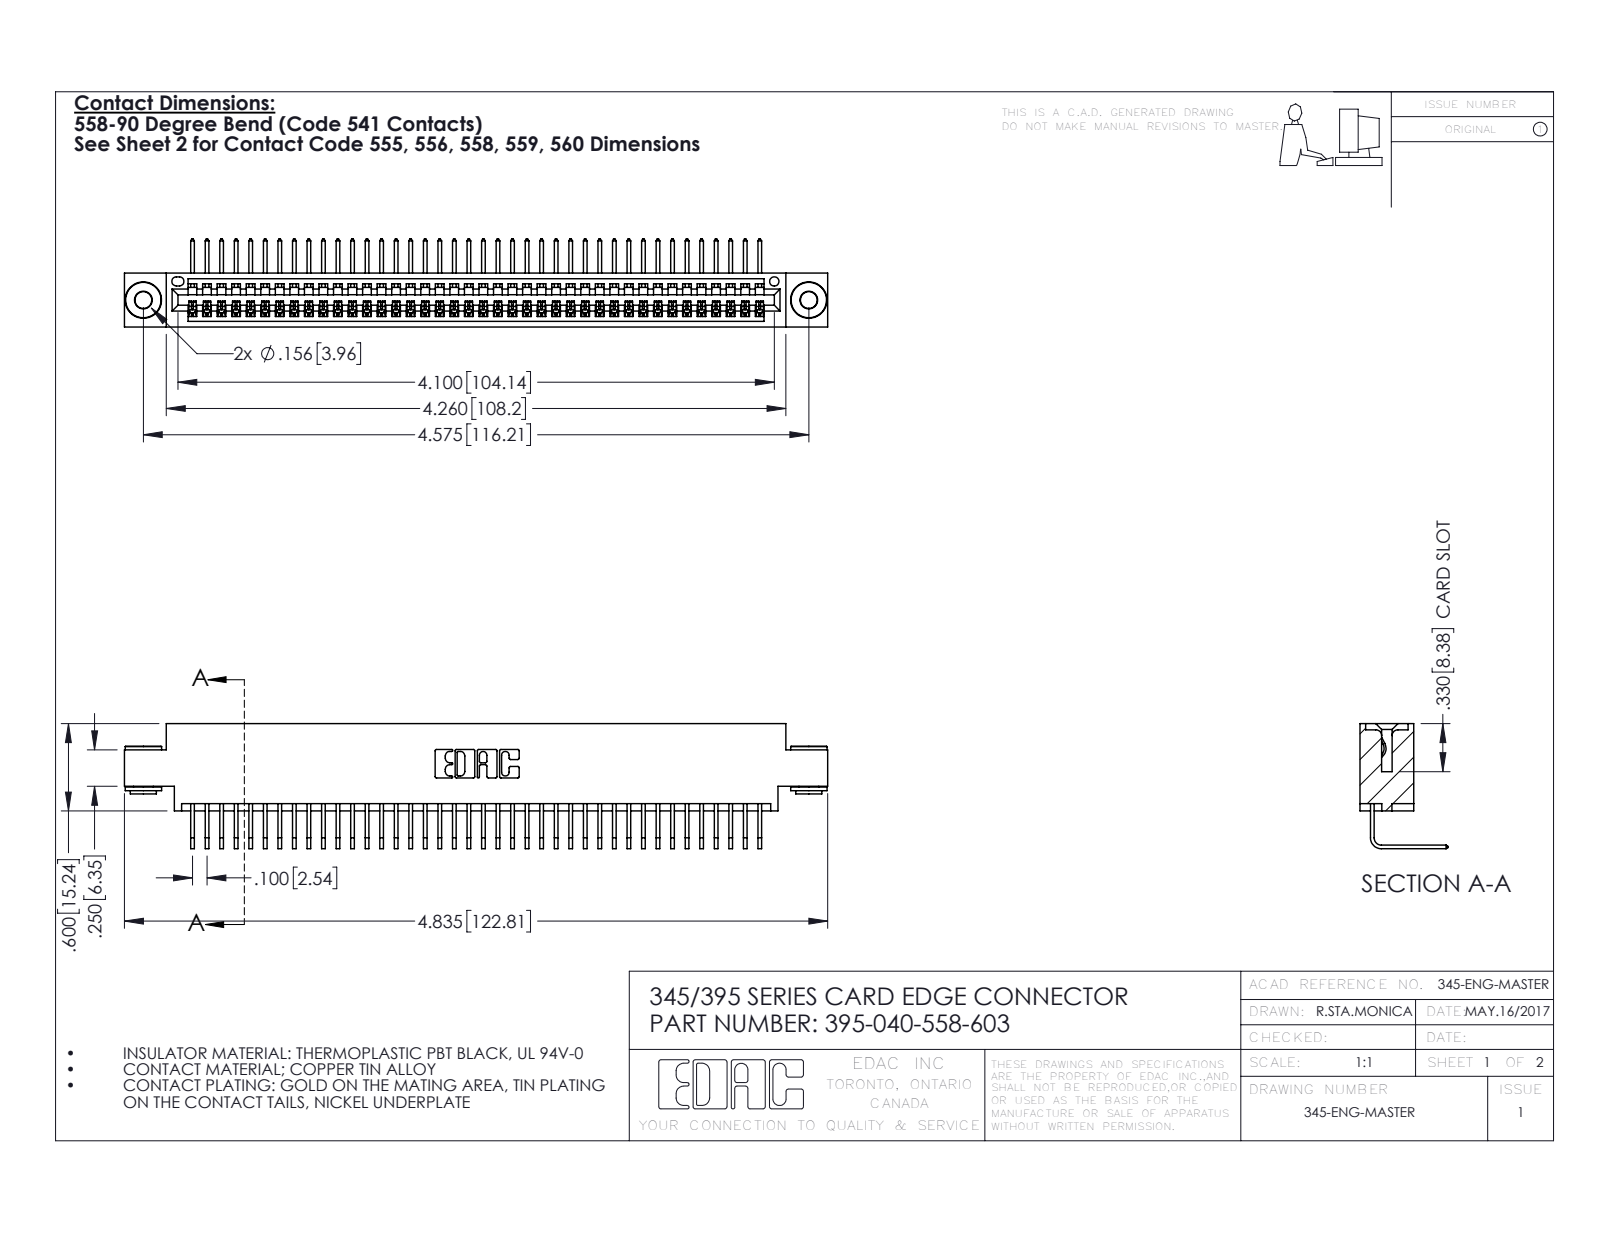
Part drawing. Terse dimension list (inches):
name: 345-292-001_558 Tail - 2; 345-250-002_345-250-002-102; 395-040-558-603; 345 Part_0.170 Offset - 0.156 Dia-TH
written by: SolidWorks 2016 (CONFIG_CONTROL_DESIGN)
unit: in
bodies: 43 solids, 2568 faces (1774 planar, 786 cylindrical, 8 other)
size: 4.835 × 0.859 × 0.605
volume: 0.713 in³; area: 25.77 in²
holes: 2× ⌀0.116, 2× ⌀0.156, 1× ⌀0.064
bosses: 2× ⌀0.25, 2× ⌀0.18, 2× ⌀0.136
rounds: 80× R0.006, 22× R0.01, 6× R0.007, 6× R0.031, 3× R0.026, 2× R0.031, 2× R0.04, 1× R0.014
face distances: 0.072, 0.298, 0.37, 0.2, 0.098, 0.272, 0.025, 0.225, 0.175, 0.149
hole spacings: 0.27, 4.339, 4.575
